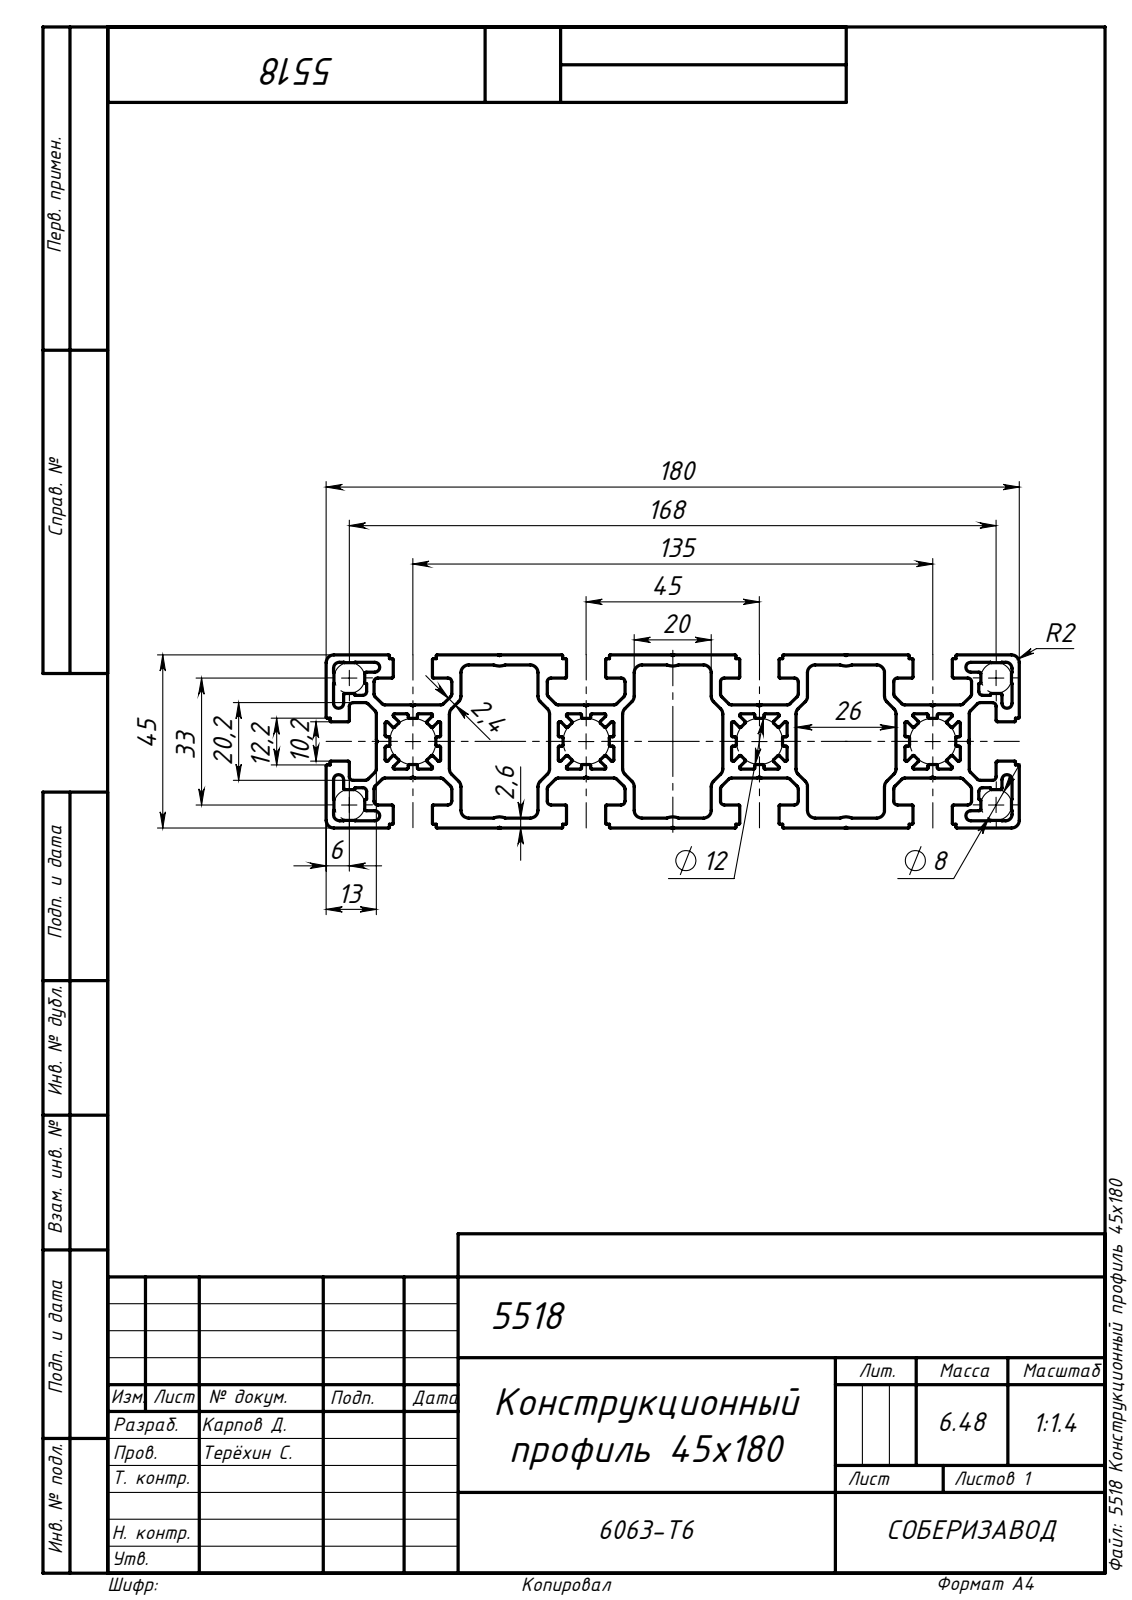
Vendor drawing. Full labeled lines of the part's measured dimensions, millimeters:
Part name (STEP PRODUCT): 5518 Конструкционный профиль 45х180
STEP written by: SolidWorks 2014 (AUTOMOTIVE_DESIGN)
Units: millimetres
Bodies: 1 solid, 902 faces (476 planar, 426 cylindrical, 0 other)
Overall size (bounding box): 1000 × 180 × 45
Volume: 2 401 000 mm³ · Surface area: 1 725 000 mm²
Partial cylindrical surfaces — rounded edges, fillets, slot ends (radius × count): R0.25 ×132, R0.3 ×120, R1 ×64, R2 ×40, R0.4 ×24, R0.35 ×8, R1.3 ×8, R4 ×6
Main face-to-face distances: 45, 32, 13, 19, 26, 2.6, 90, 42.4, 10.4, 29.4
